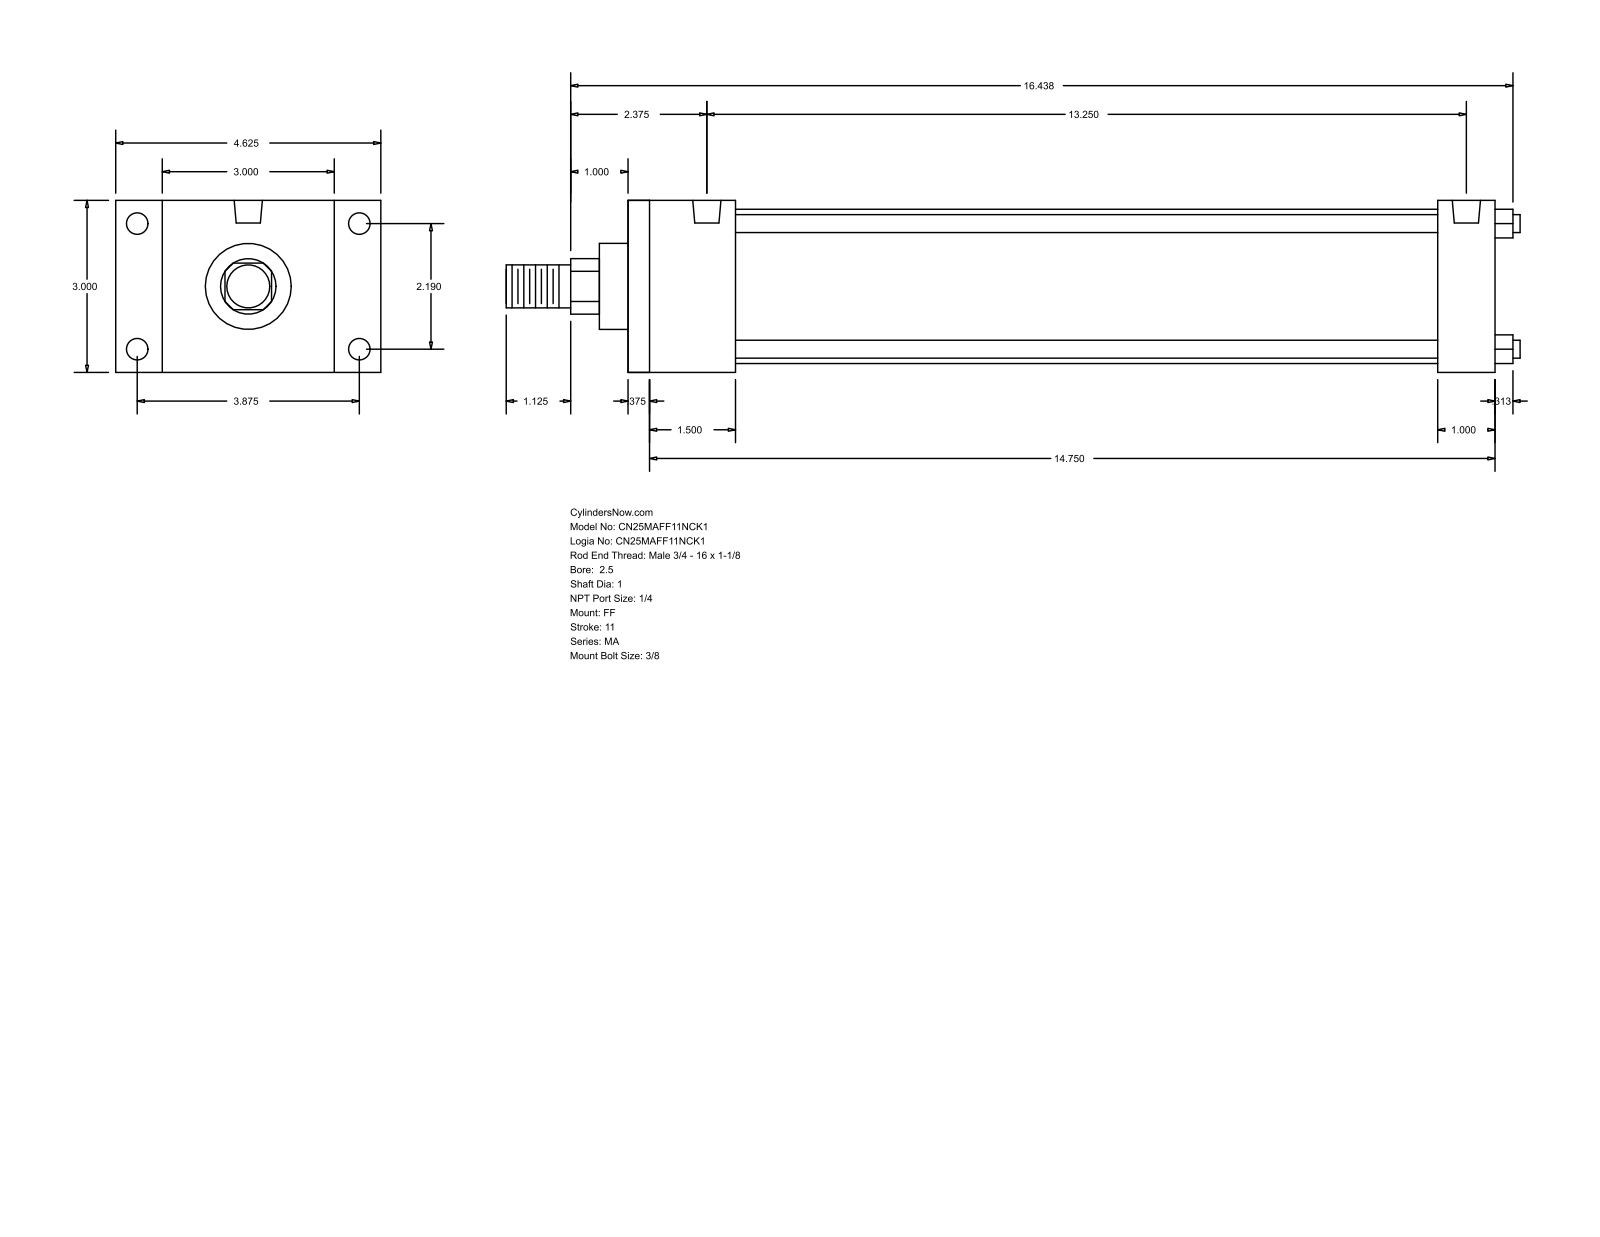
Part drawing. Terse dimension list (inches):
name: MA_FF__0250_1
written by: GSSL Pune (CONFIG_CONTROL_DESIGN)
unit: in
bodies: 0 solids, 92 faces (64 planar, 28 cylindrical, 0 other)
size: 17.687 × 4.625 × 3
holes: 4× ⌀0.313, 4× ⌀0.375, 2× ⌀0.492
bosses: 4× ⌀0.313, 1× ⌀2.69, 1× ⌀1.5, 1× ⌀1, 1× ⌀0.75
rounds: 1× R0.484
face distances: 3, 15.125, 14.75, 0.375, 1, 1.875, 14.125, 1.5, 13.75, 12.25
hole spacings: 2.19, 3.875, 4.451, 13.25
